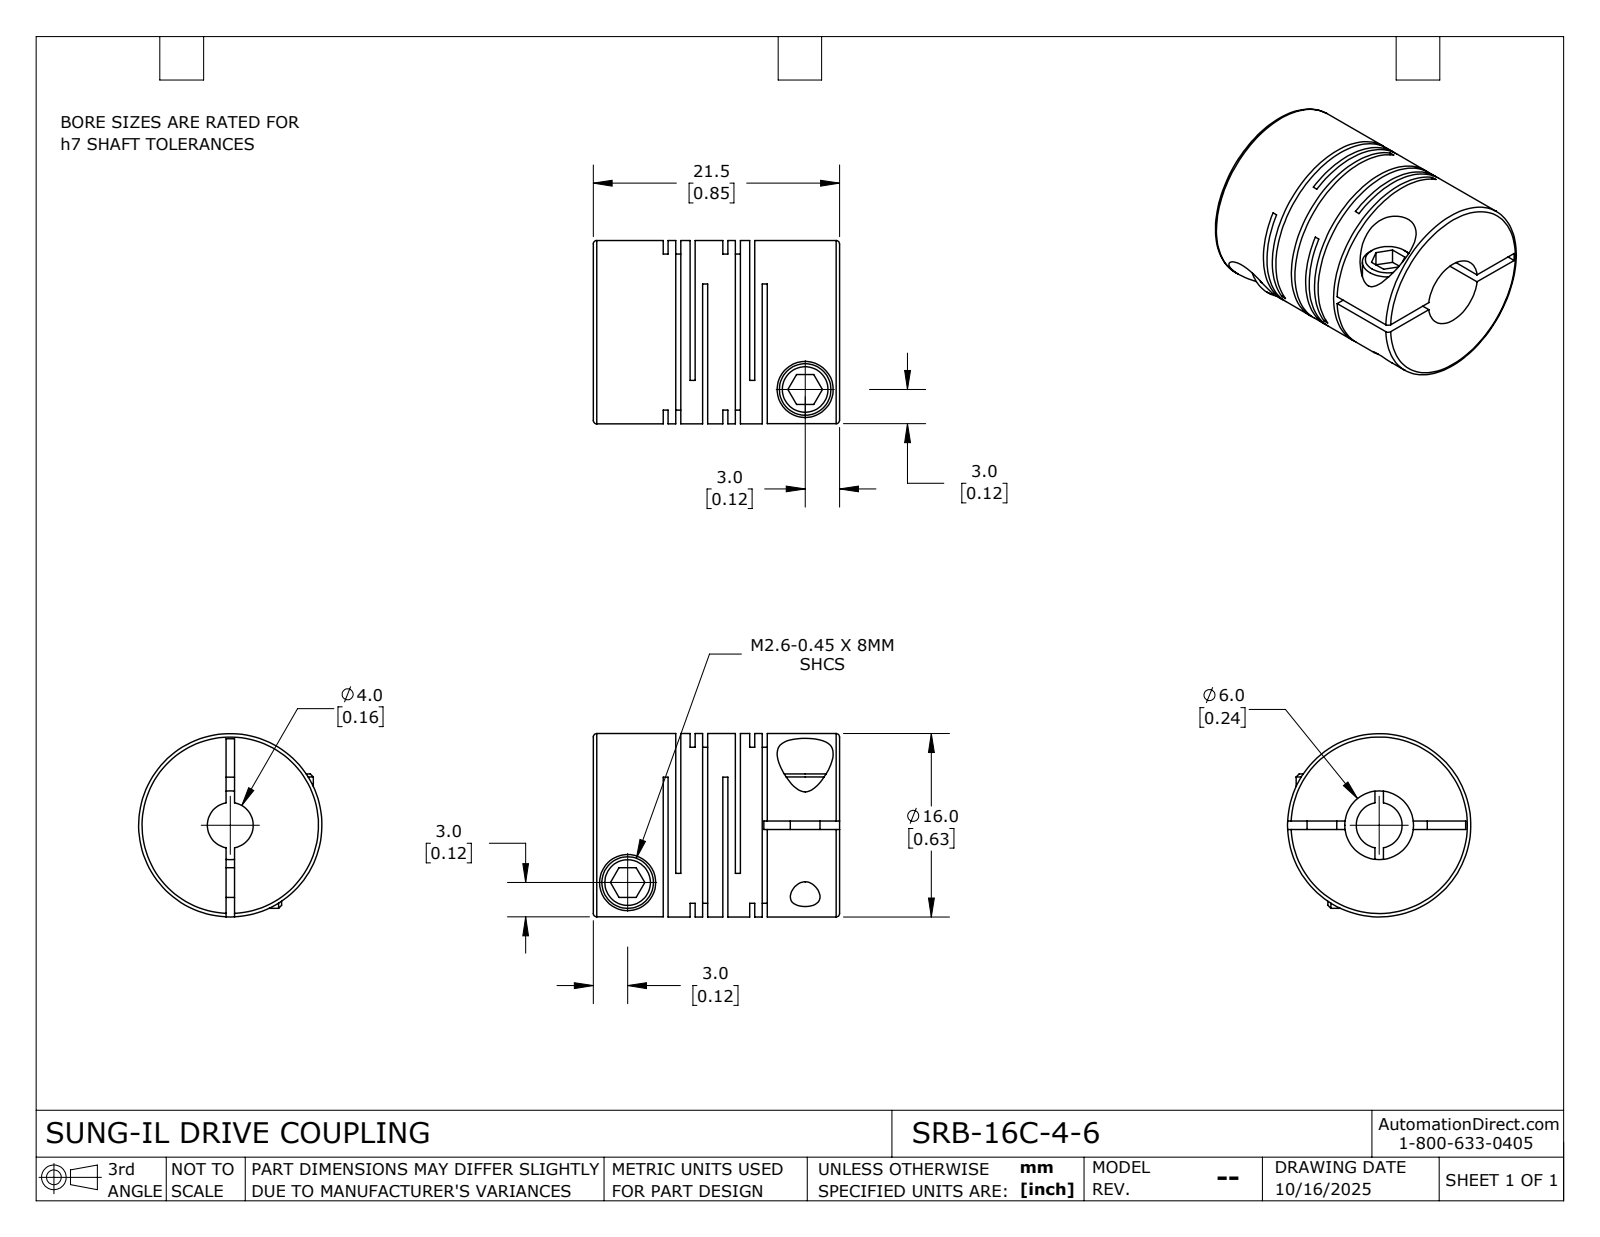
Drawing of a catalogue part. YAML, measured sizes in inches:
part_name: "SRB-16C-4-6"
step_written_by: "SolidWorks 2024 (CONFIG_CONTROL_DESIGN)"
units: inches
bodies: {solids: 1, faces: 115, planar: 60, cylindrical: 42, other: 13}
overall_size: [0.846, 0.63, 0.63]
volume: 0.191
surface_area: 6.6
round_holes:
  - {diameter: 0.102, count: 2}
  - {diameter: 0.193, count: 2}
  - {diameter: 0.157, count: 1}
  - {diameter: 0.236, count: 1}
round_bosses_or_shafts:
  - {diameter: 0.177, count: 2}
  - {diameter: 0.63, count: 1}
face_to_face_distances: [0.043, 0.093, 0.017, 0.205, 0.026, 0.075, 0.188, 0.049, 0.162, 0.113]
